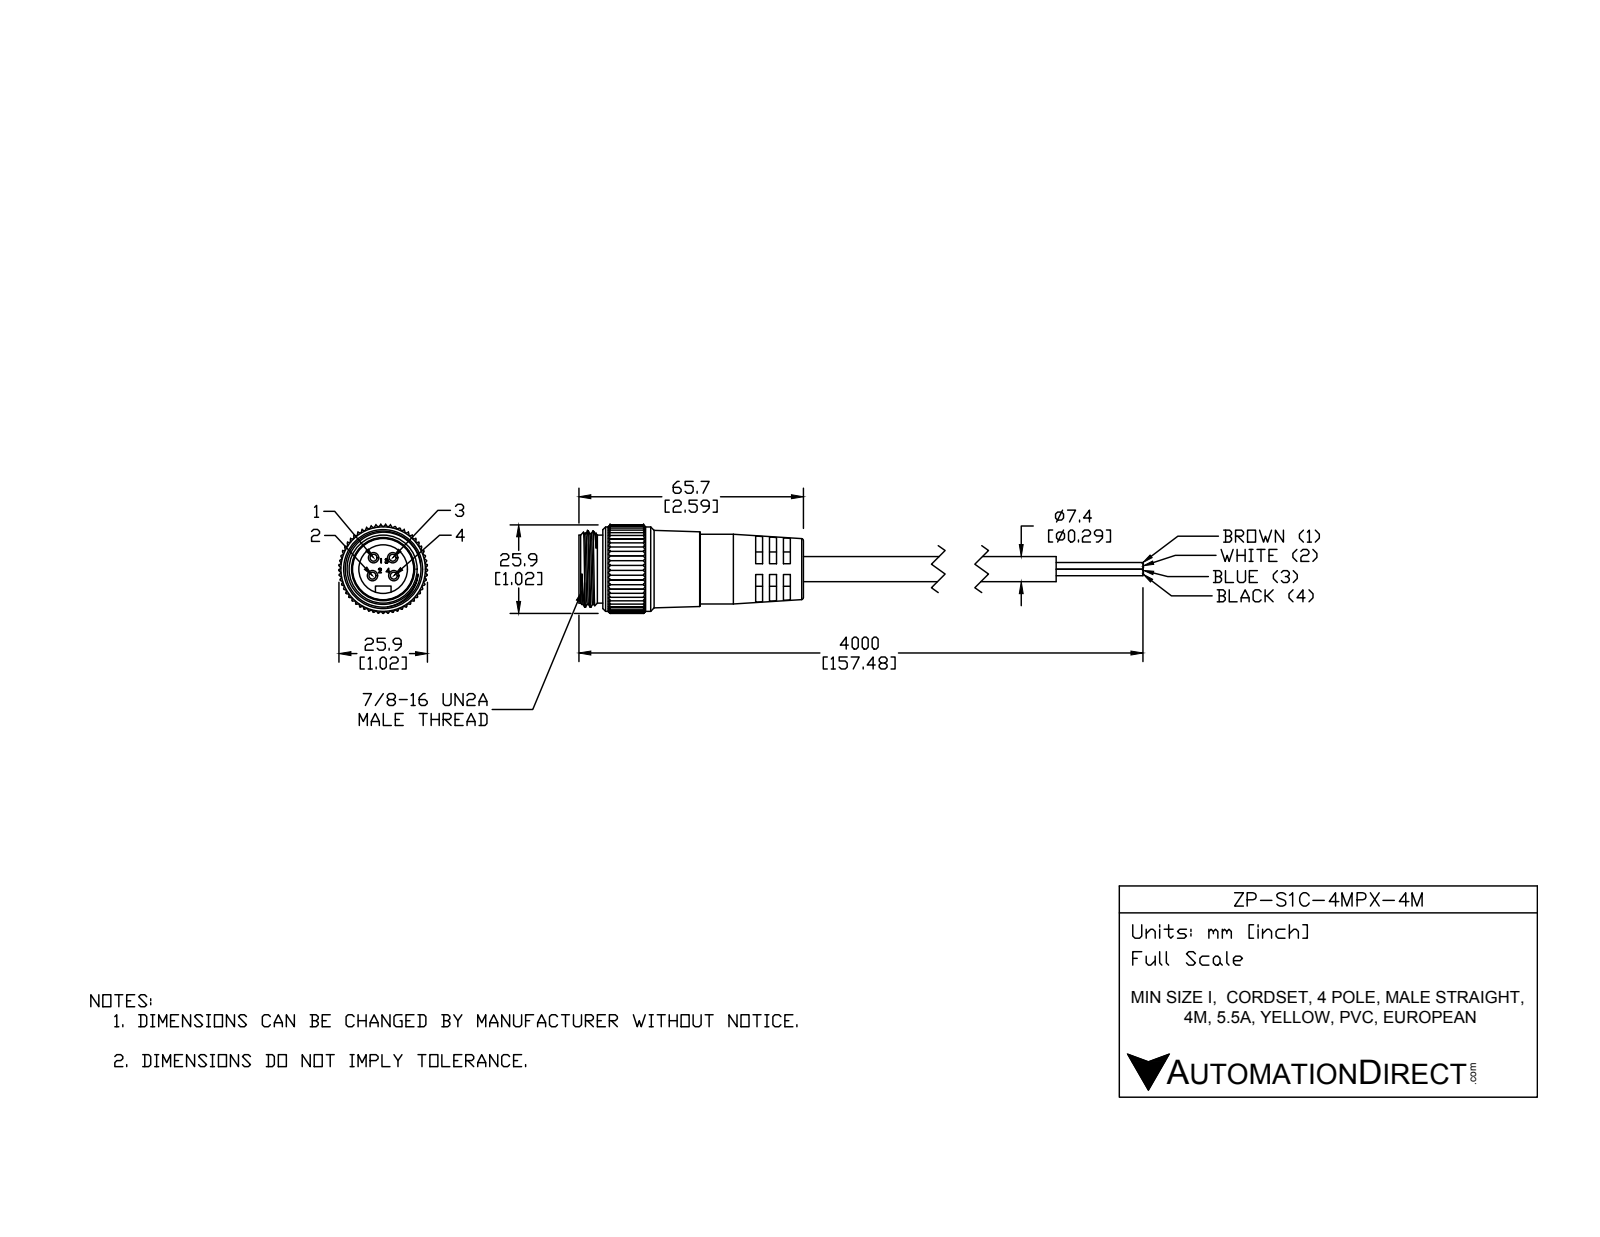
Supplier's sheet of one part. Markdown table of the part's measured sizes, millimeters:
| quantity | value |
| --- | --- |
| part name | ZP-S1C-4MPX-4M |
| STEP written by | SolidWorks 2015 (AUTOMOTIVE_DESIGN) |
| units | millimeters |
| bodies | 6 solids, 606 faces (218 planar, 326 cylindrical, 62 other) |
| overall size | 115.9 × 25.84 × 25.83 |
| volume | 26 095 mm³ |
| surface area | 13 335 mm² |
| round holes (diameter × count) | 14.22 × 1, 17.88 × 1, 19.96 × 1, 20.45 × 1, 21 × 1 |
| round bosses / shafts (diameter × count) | 3.05 × 4, 2 × 4, 24.68 × 1, 22.22 × 1, 20.4 × 1, 19.5 × 1, 9.91 × 1 |
| partial cylindrical surfaces (radius × count) | 0.25 × 165, 2.29 × 1, 5.25 × 1, 12.93 × 1 |
| main face-to-face distances | 2, 4.04, 13.88, 11.88, 2.04, 9.84, 6.04, 7.84, 2.02, 8.06 |
